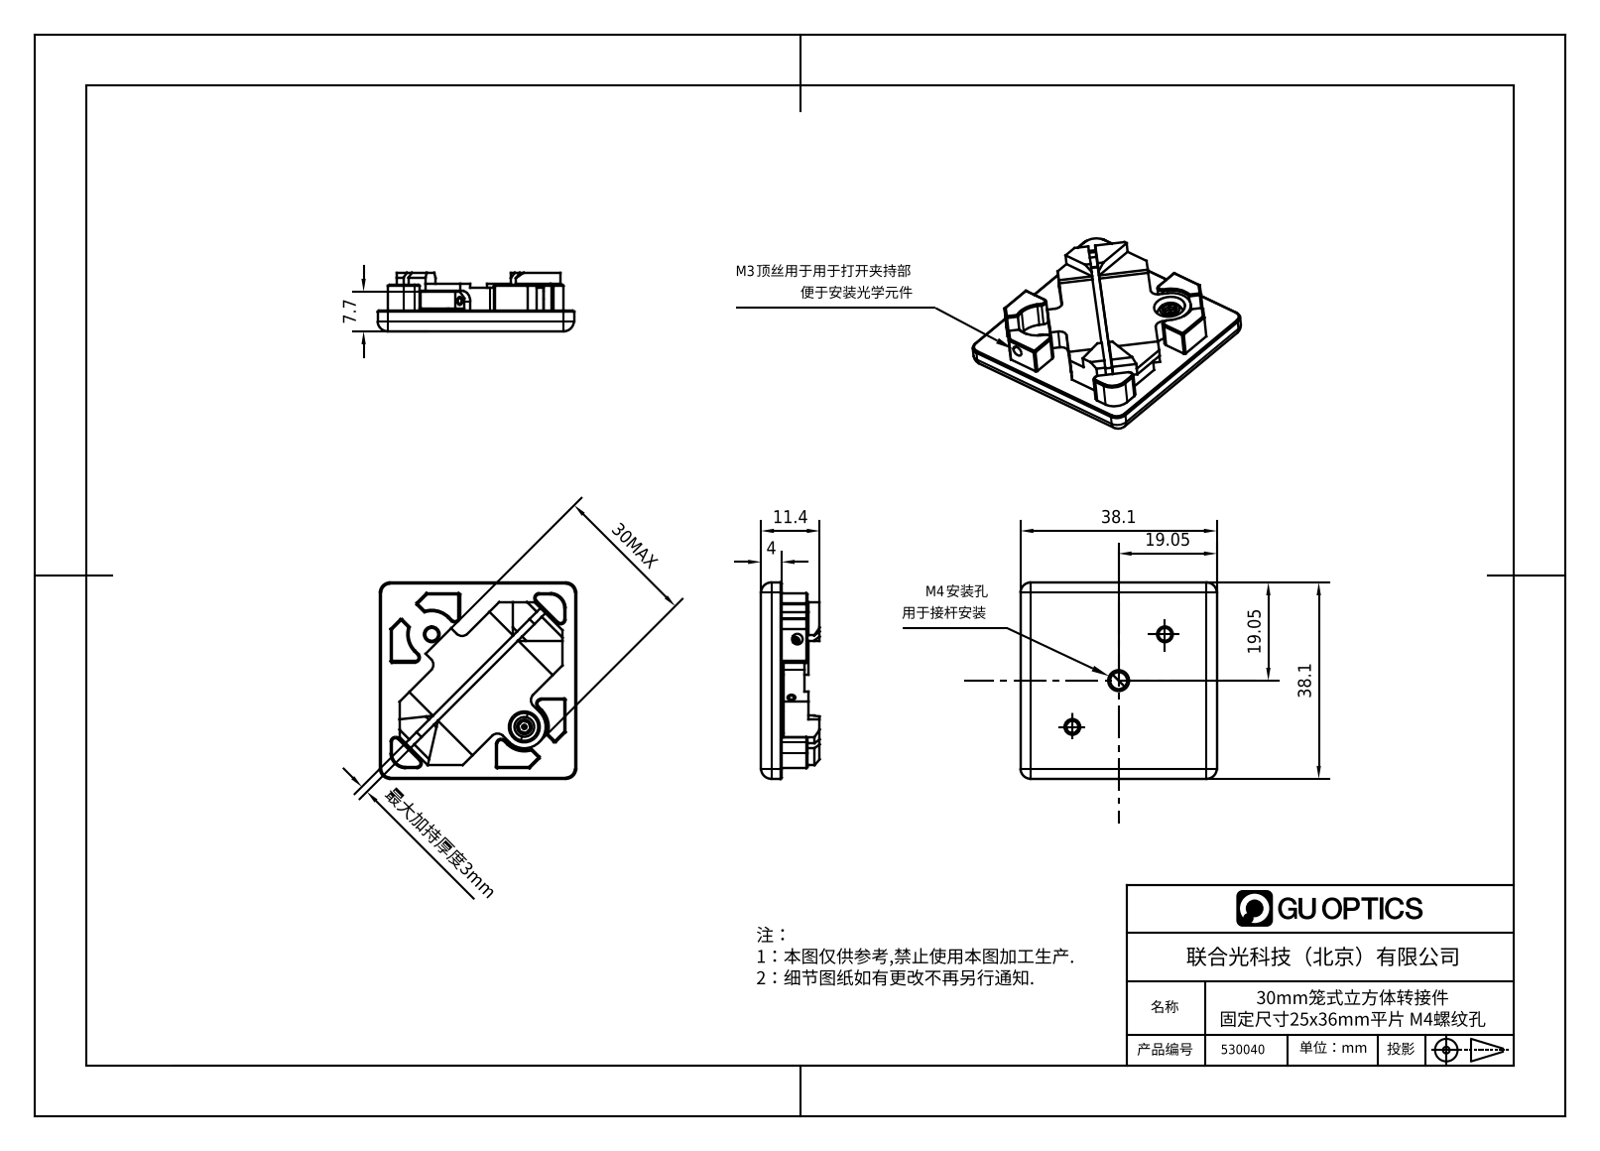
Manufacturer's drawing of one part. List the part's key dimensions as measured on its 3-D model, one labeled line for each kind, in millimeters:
Part name (STEP PRODUCT): 2.2.7.38_L30F-ZF2J_30mm笼式二向色性滤光片接杆式安装座，适合长度26-43mm方形镜片
STEP written by: SolidWorks 2018 (AUTOMOTIVE_DESIGN)
Units: millimetres
Bodies: 0 solids, 264 faces (160 planar, 55 cylindrical, 49 other)
Overall size (bounding box): 38.1 × 38.1 × 11.4
Round holes (diameter × count): ⌀2.5 ×3, ⌀1.5 ×2, ⌀2.05 ×2, ⌀3.3 ×1, ⌀6 ×1
Partial cylindrical surfaces — rounded edges, fillets, slot ends (radius × count): R2 ×10, R1 ×8, R1.5 ×4, R3 ×2, R4.5 ×2, R4.14 ×1
Main face-to-face distances: 4, 8.4, 4.4, 0.6, 9, 2.05, 36.05, 3.8, 7.56, 3.56
Hole centre spacings: 12.51, 12.7, 16.1, 25, 25.4
